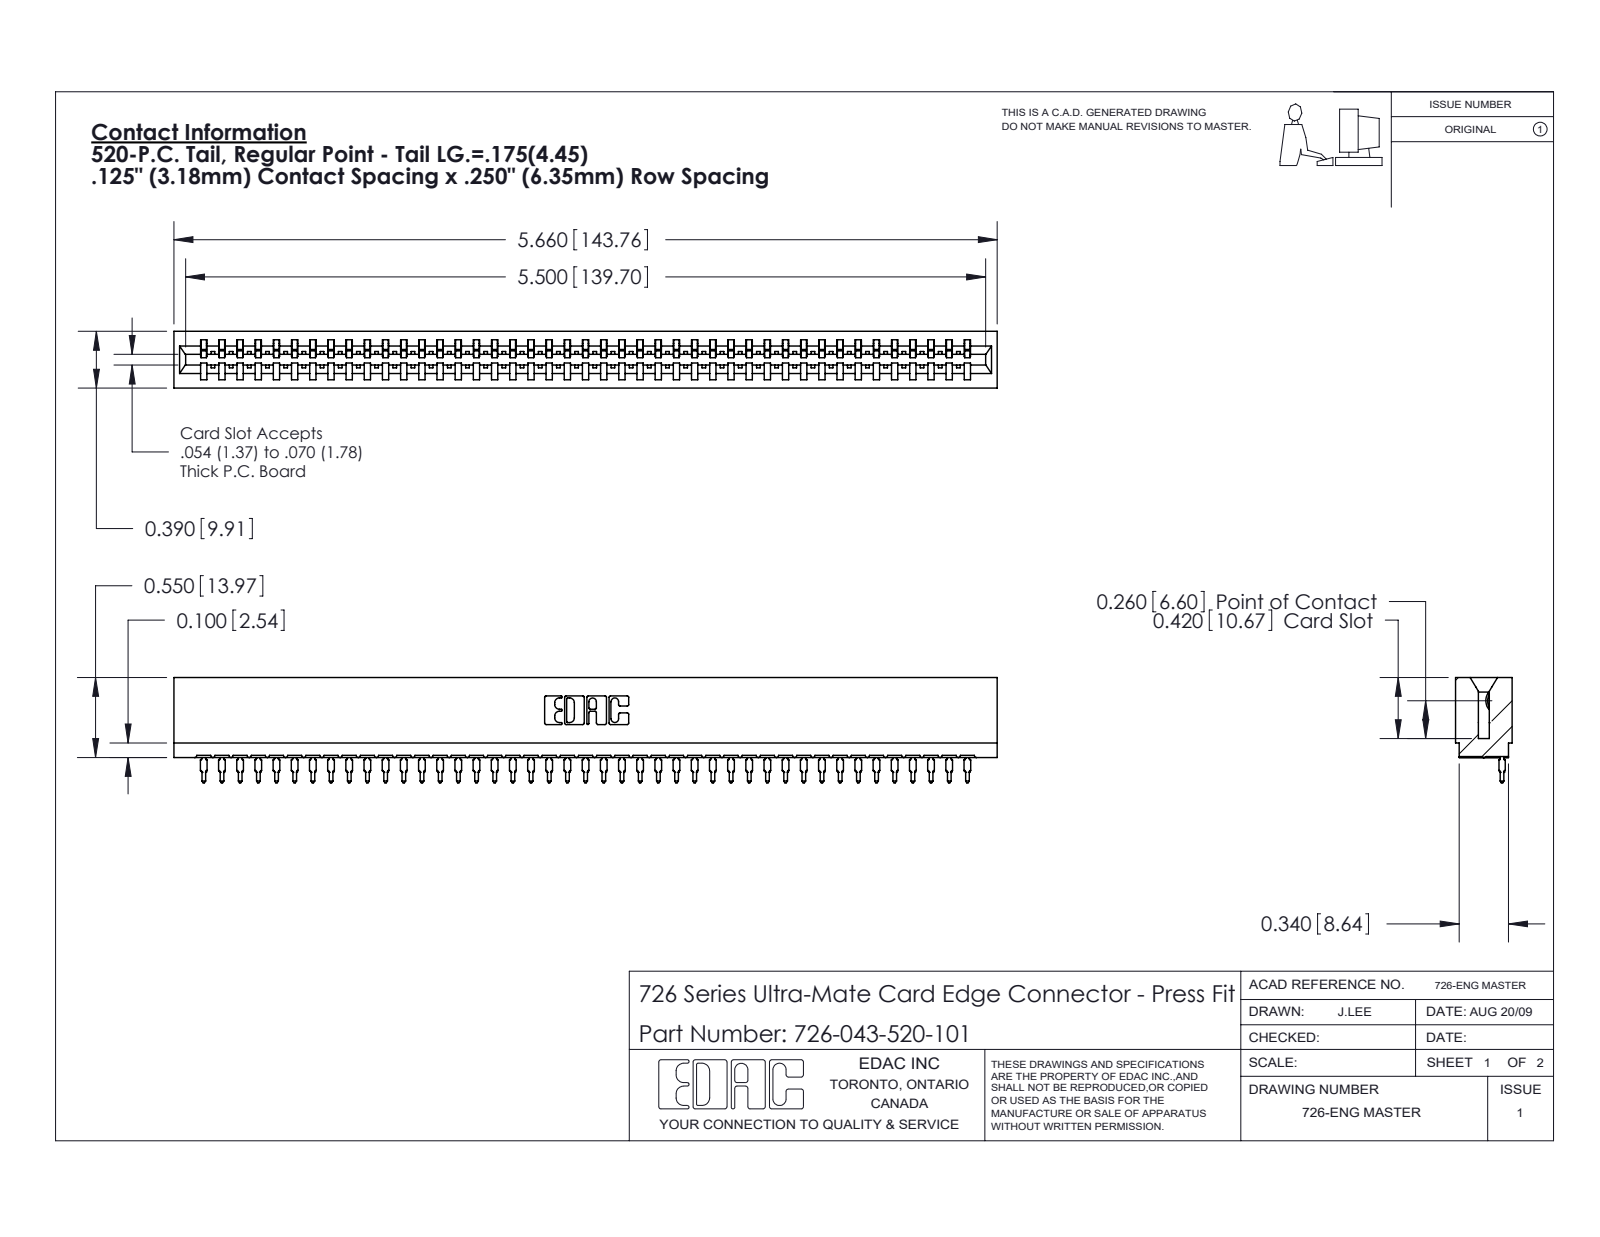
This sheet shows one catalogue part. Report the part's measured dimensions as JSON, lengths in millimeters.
{"part_name": "746-292-001_520; 726-043-520-101; 726 Part_.515 Slot Depth - 01", "step_written_by": "SolidWorks 2020 (CONFIG_CONTROL_DESIGN)", "units": "millimeters", "bodies": {"solids": 44, "faces": 4741, "planar": 2764, "cylindrical": 859, "other": 1118}, "overall_size": [143.8, 18.4, 9.9], "volume_mm3": 12800, "surface_area_mm2": 19200, "partial_cylinders_radius": [[0.5, 86], [0.4, 44], [0.3, 22], [0.2, 6], [0.8, 6], [0.1, 4], [0.3, 4], [0.7, 3]], "face_to_face_distances": [1.4, 8.5, 9.9, 0.6, 7.8, 6.4, 7, 9.3, 0.8, 4.4]}
